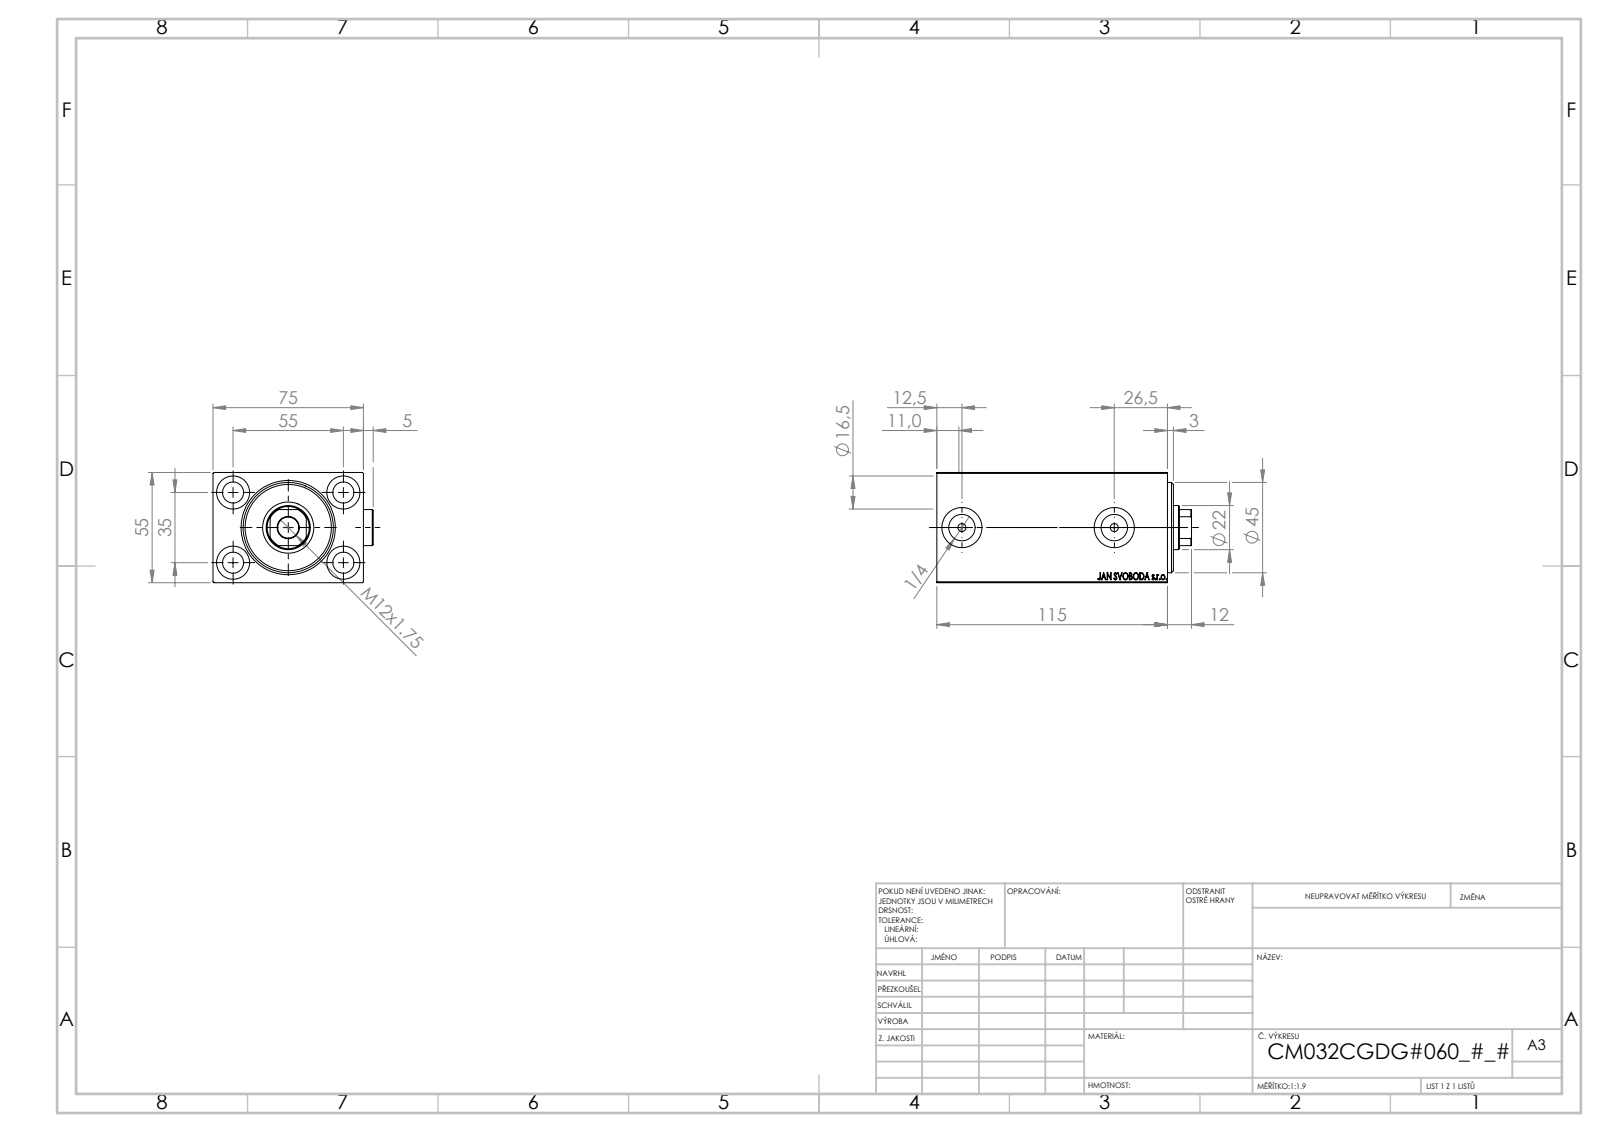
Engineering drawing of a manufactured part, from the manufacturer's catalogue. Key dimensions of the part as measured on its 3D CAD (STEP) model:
Part name (STEP PRODUCT): V450CM_VC_B; Zatka_OIL_PORT; V450CM_C_Body; V450CM_C_VCP
STEP written by: SolidWorks 2019 (CONFIG_CONTROL_DESIGN)
Units: millimetres
Bodies: 5 solids, 916 faces (442 planar, 76 cylindrical, 398 other)
Overall size (bounding box): 127 × 79.9 × 55
Volume: 398 336 mm³ · Surface area: 85 707 mm²
Round holes (diameter × count): ⌀10.5 ×5, ⌀16.5 ×4, ⌀4 ×2, ⌀13.16 ×2, ⌀20 ×2, ⌀22 ×1, ⌀25.5 ×1, ⌀32 ×1, ⌀34 ×1, ⌀45 ×1
Round bosses / shafts (diameter × count): ⌀18 ×2
Partial cylindrical surfaces — rounded edges, fillets, slot ends (radius × count): R10.5 ×1
Main face-to-face distances: 55, 75, 5, 10, 105, 115, 110, 100, 74.9, 93
Hole centre spacings: 32.6, 35, 55, 65.19, 76
